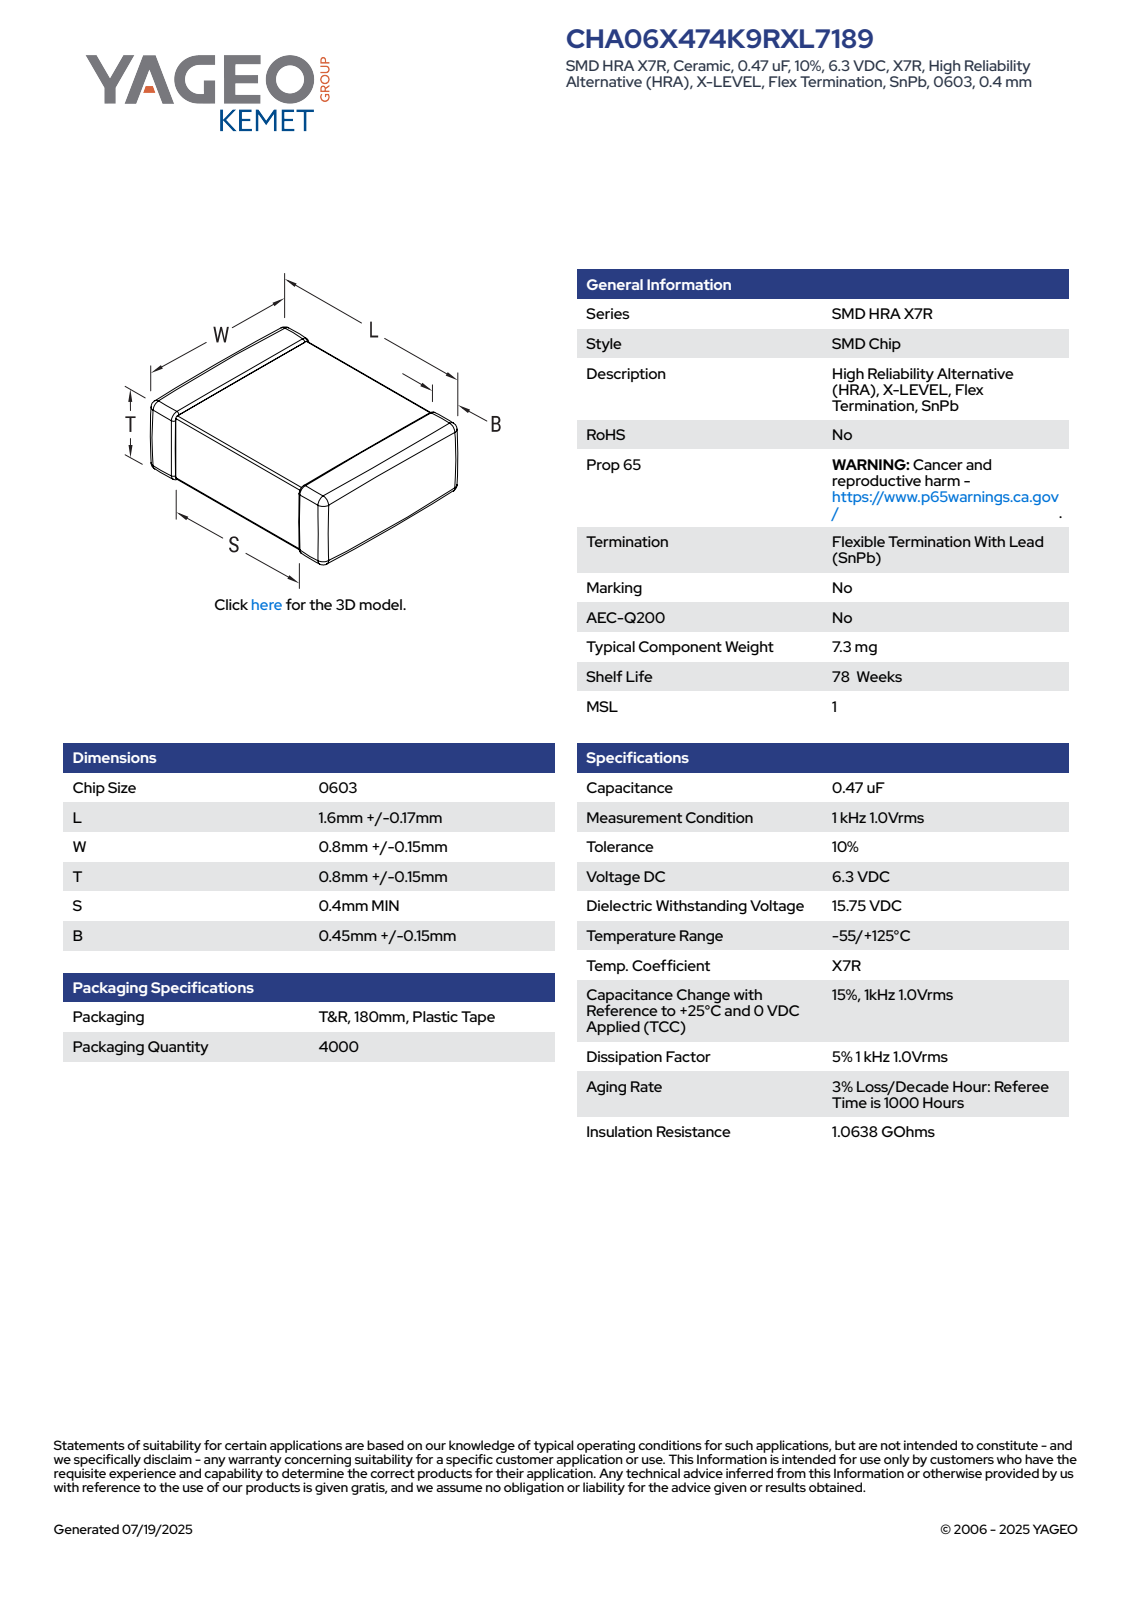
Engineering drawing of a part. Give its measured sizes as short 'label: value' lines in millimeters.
name: CCSM_STD_0603_L1.77W0.95T0.95S0.8B0.6
written by: SolidWorks 2021 (AUTOMOTIVE_DESIGN)
unit: mm
bodies: 4 solids, 125 faces (71 planar, 38 cylindrical, 16 other)
size: 1.77 × 0.95 × 0.95
volume: 2 mm³; area: 9 mm²
face distances: 0.93, 0.95, 0.91, 1.77, 0.94, 0.92, 0.82, 0.96, 0.81, 0.84
